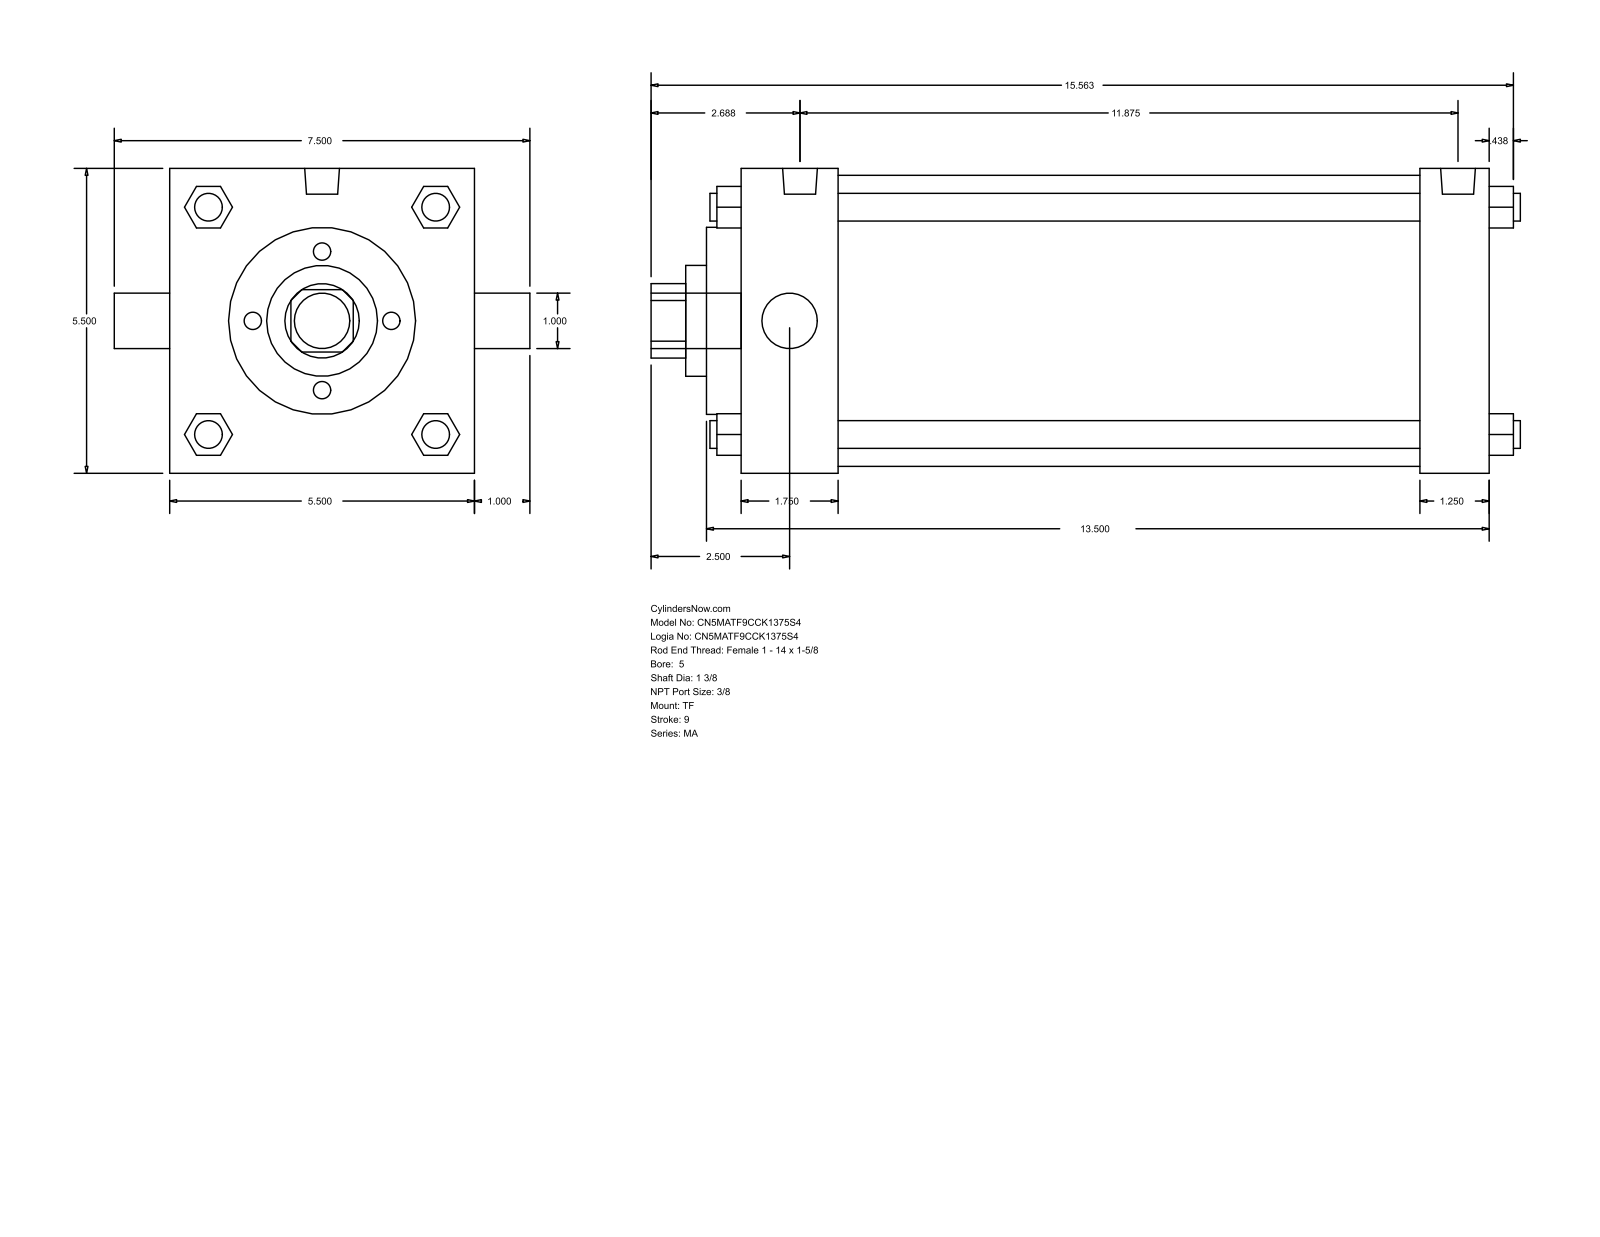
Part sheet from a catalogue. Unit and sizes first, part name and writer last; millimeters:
Units: millimetres
Overall size (bounding box): 398.46 × 190.5 × 139.7
Round holes (diameter × count): ⌀25.4 ×1, ⌀34.92 ×1, ⌀50.8 ×1, ⌀85.72 ×1, ⌀133.35 ×1
Round bosses / shafts (diameter × count): ⌀12.7 ×4, ⌀11.11 ×3, ⌀15.93 ×2, ⌀25.4 ×1
Partial cylindrical surfaces — rounded edges, fillets, slot ends (radius × count): R17.06 ×1
Main face-to-face distances: 139.7, 342.91, 311.16, 31.75, 44.45, 266.71, 298.46, 15.87, 60.32, 327.03
Bodies: 0 solids, 122 faces (93 planar, 29 cylindrical, 0 other)
Part name (STEP PRODUCT): MA_TF__0500_1.375
STEP written by: GSSL Pune (CONFIG_CONTROL_DESIGN)
